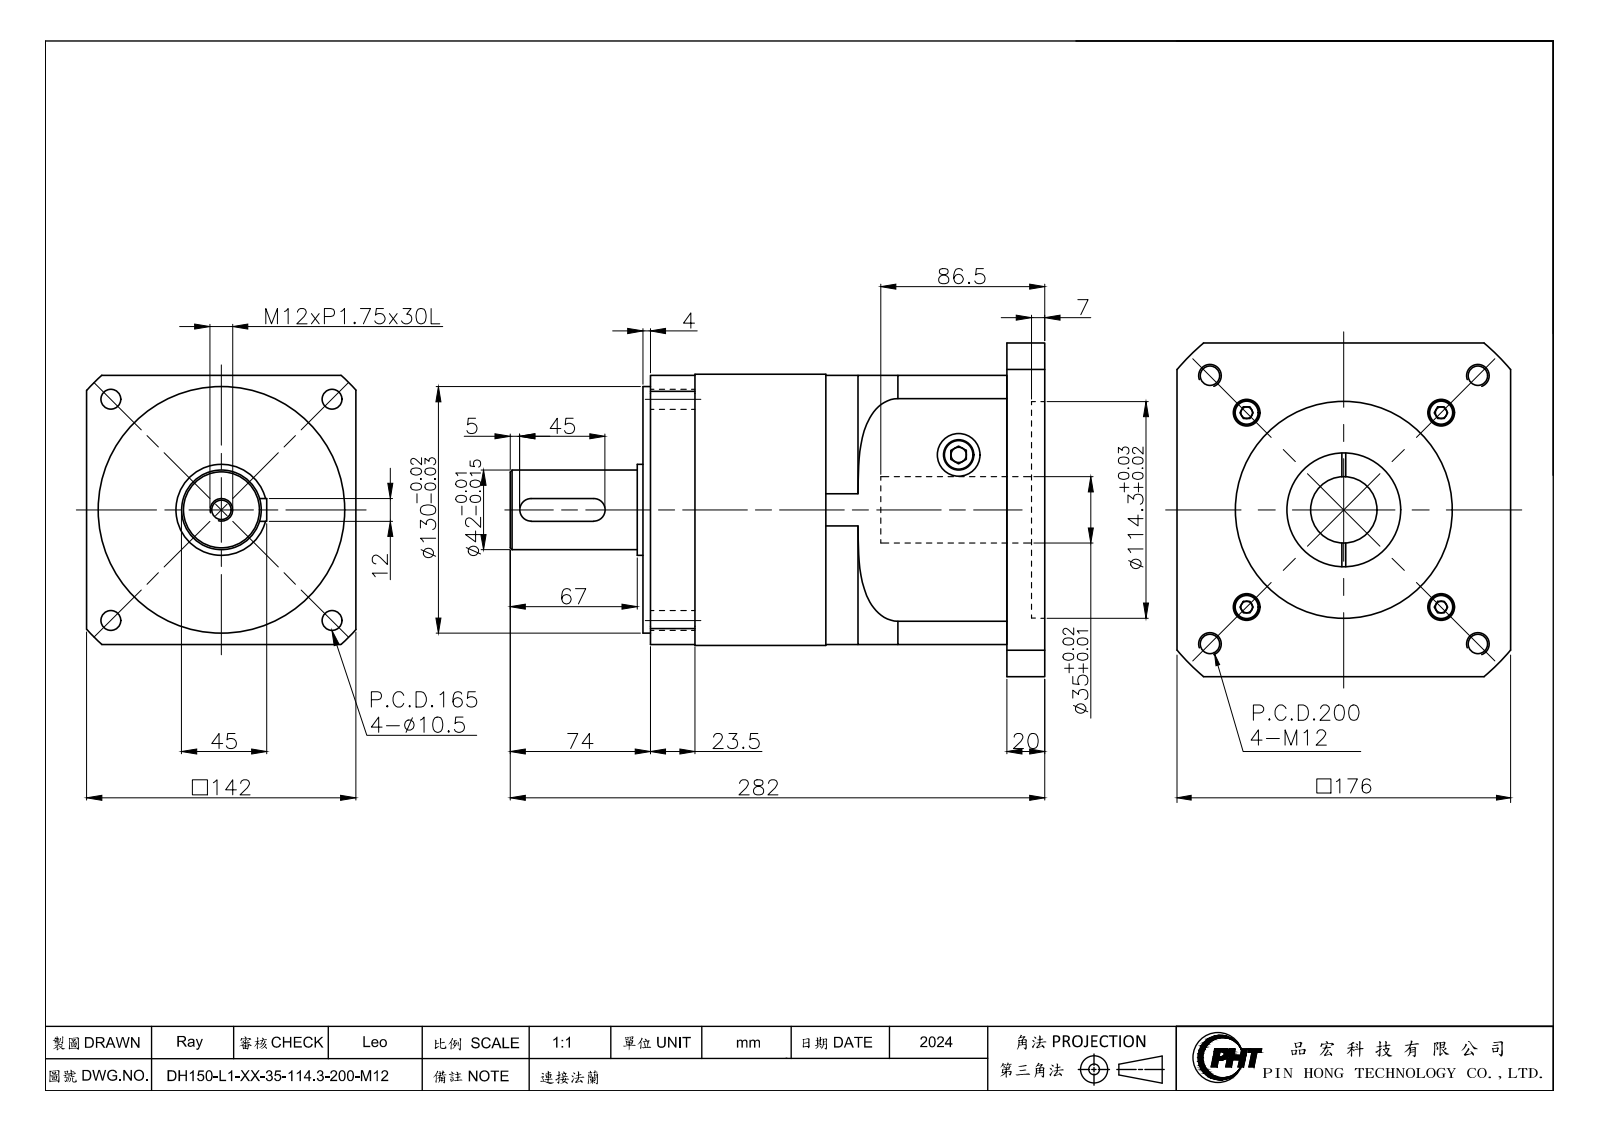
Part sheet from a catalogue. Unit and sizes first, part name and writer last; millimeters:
Units: millimetres
Overall size (bounding box): 282 × 176 × 176
Round holes (diameter × count): ⌀14 ×8, ⌀10.2 ×5, ⌀6.8 ×4, ⌀9 ×4, ⌀10.5 ×4, ⌀15 ×4, ⌀22.5 ×2, ⌀35 ×1, ⌀60 ×1, ⌀92 ×1, ⌀110 ×1, ⌀114.3 ×1
Round bosses / shafts (diameter × count): ⌀12.2 ×12, ⌀8 ×4, ⌀143 ×1, ⌀130 ×1, ⌀74 ×1, ⌀48 ×1, ⌀42 ×1
Partial cylindrical surfaces — rounded edges, fillets, slot ends (radius × count): R6 ×2, R72 ×1, R92.5 ×1, R95 ×1, R115 ×1
Main face-to-face distances: 142, 20, 17, 159, 192, 212, 5, 7, 205, 13
Hole centre spacings: 66, 19.2, 25.37, 40.07, 84.48, 91.35, 93.34, 104.59
Volume: 3 704 000 mm³ · Surface area: 307 825 mm²
Bodies: 2 solids, 353 faces (164 planar, 141 cylindrical, 48 other)
Part name (STEP PRODUCT): DH150-L1-XX-35-114.3-200-M12(連接法蘭)_2024
STEP written by: SolidWorks 2016 (CONFIG_CONTROL_DESIGN)
